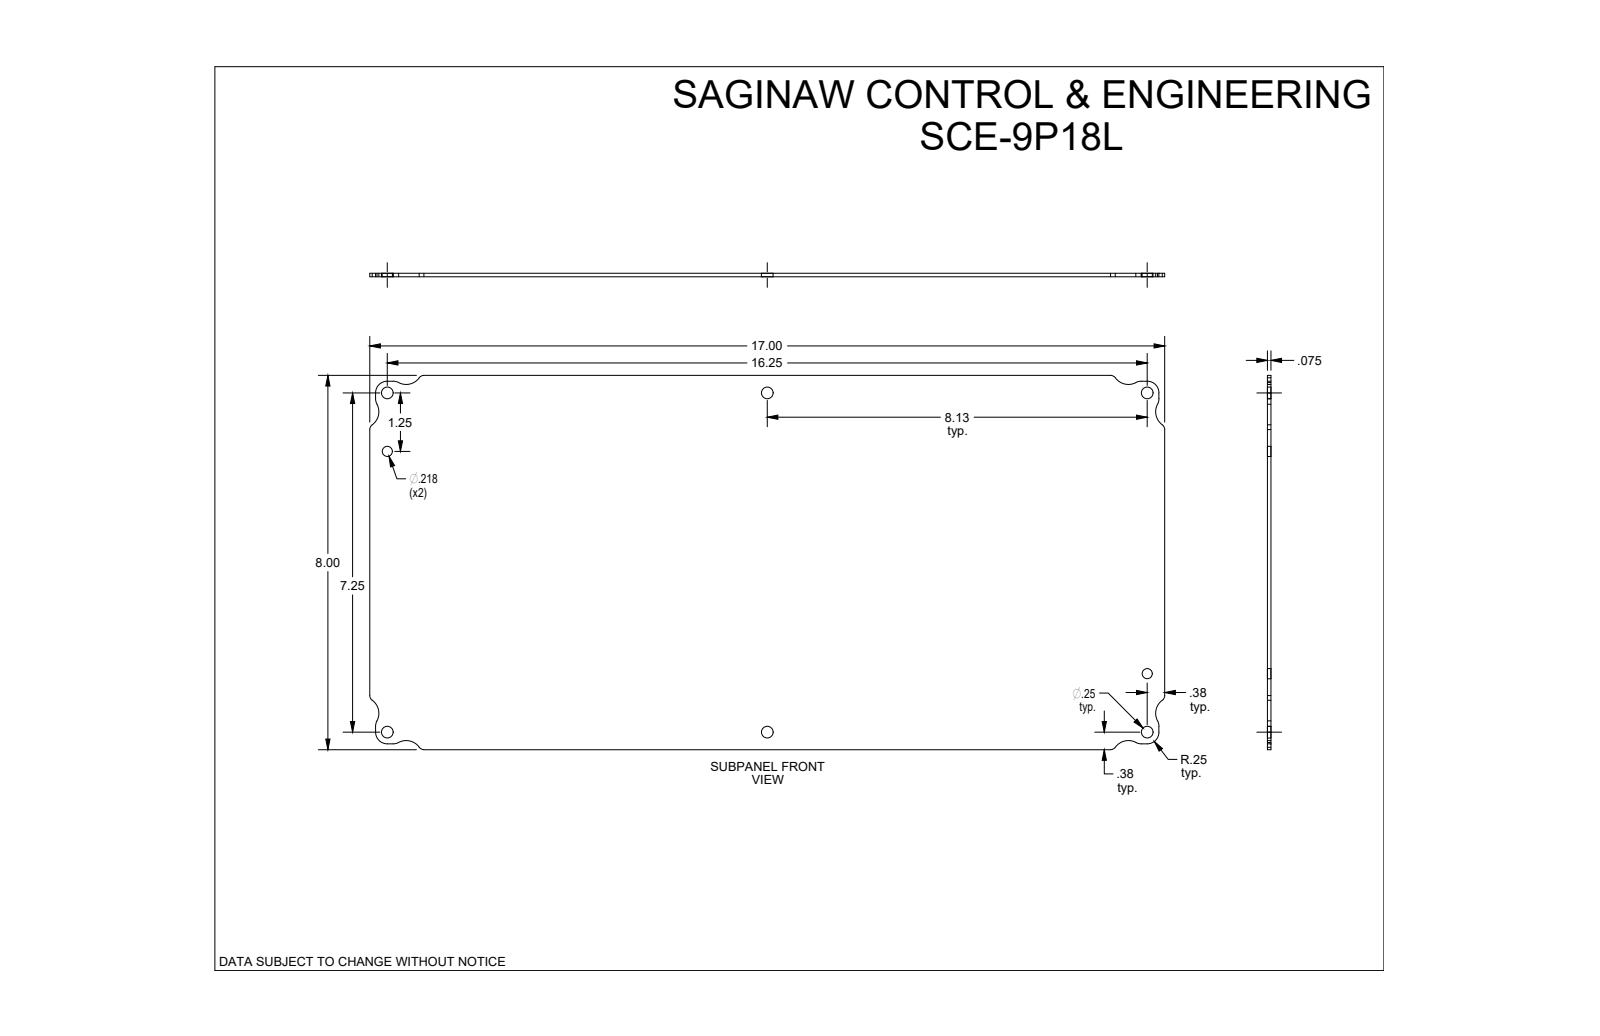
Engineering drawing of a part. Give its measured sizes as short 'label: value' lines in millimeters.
name: SCE-9P18L
written by: SolidWorks 2019 (CONFIG_CONTROL_DESIGN)
unit: mm
bodies: 1 solid, 50 faces (14 planar, 36 cylindrical, 0 other)
size: 431.8 × 203.2 × 1.9
volume: 165 200 mm³; area: 176 100 mm²
holes: 6× ⌀6.4, 2× ⌀5.5
rounds: 12× R6.4, 8× R3.2, 8× R8.7
face distances: 1.9, 203.2, 431.8, 3.2, 200, 428.6, 196.9, 425.5
hole spacings: 206.4, 276.6, 184.2, 31.8, 152.4, 208.8, 256.5, 412.8
